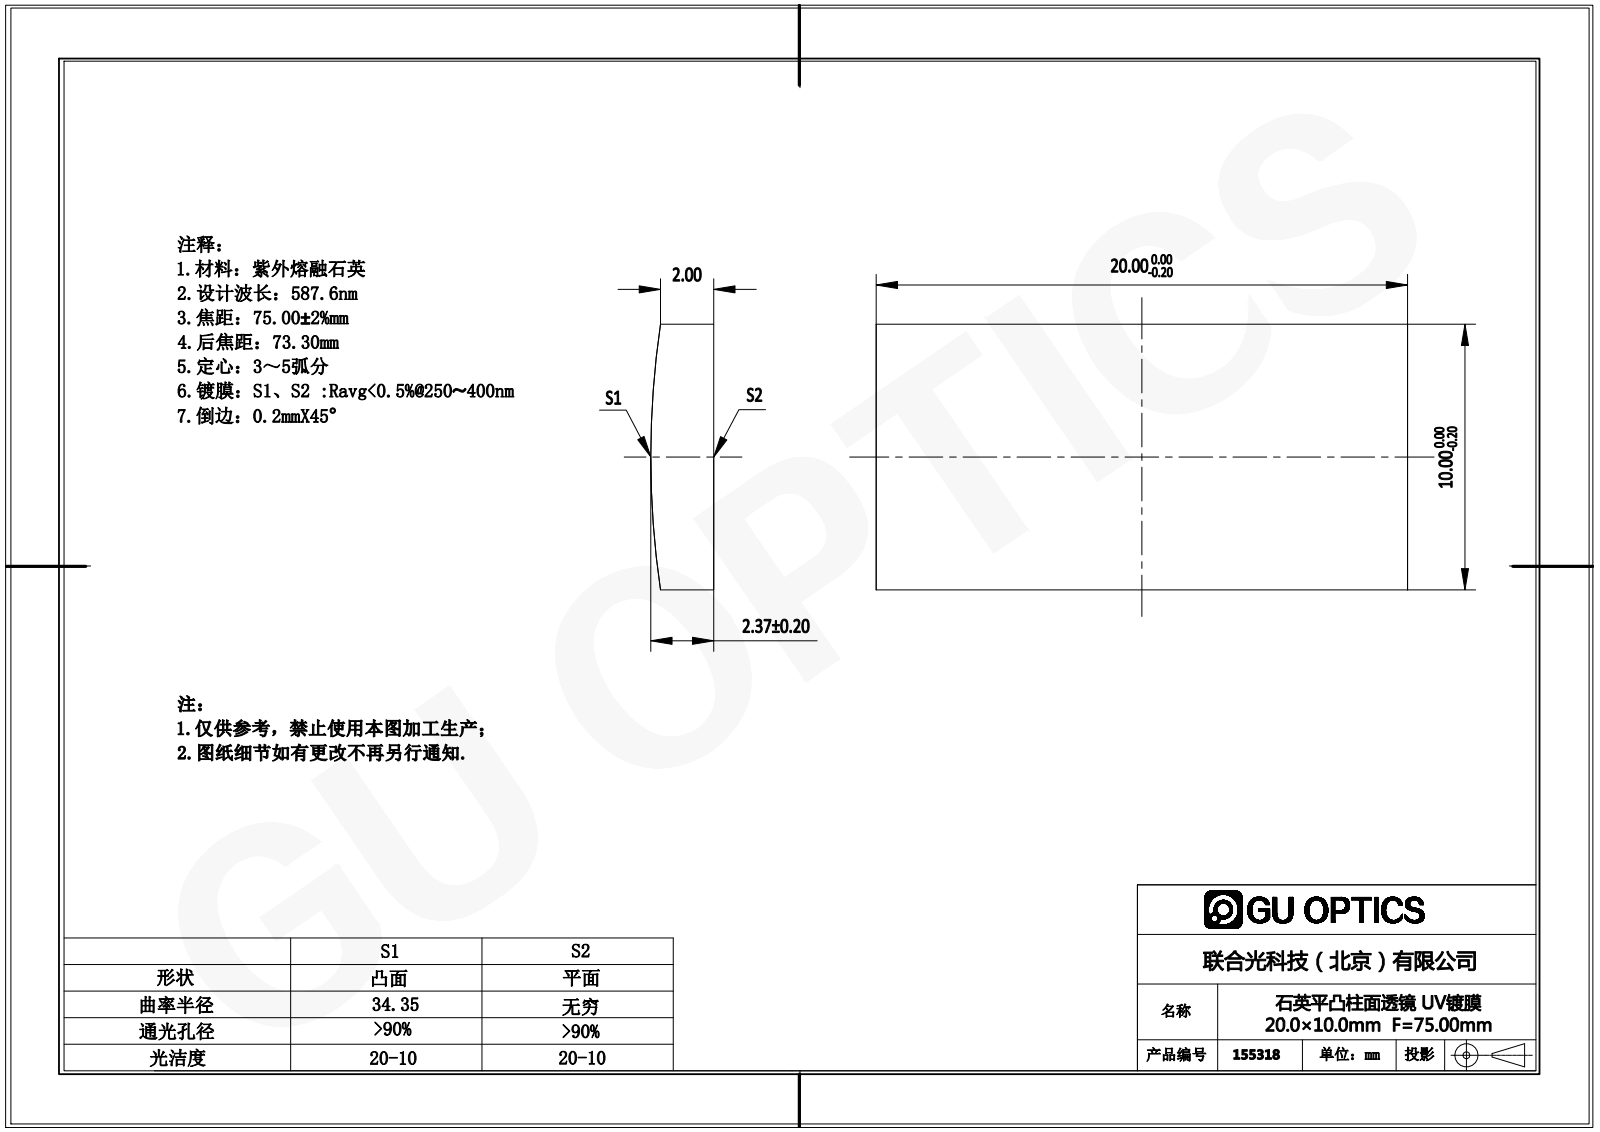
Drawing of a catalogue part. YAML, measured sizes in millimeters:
part_name: "155284"
step_written_by: "SolidWorks 2016 (AUTOMOTIVE_DESIGN)"
units: millimeters
bodies: {solids: 1, faces: 6, planar: 5, cylindrical: 1, other: 0}
overall_size: [20, 10, 2.37]
volume: 450
surface_area: 526
partial_cylinders:
  - {radius: 34.35, count: 1}
face_to_face_distances: [10, 20]
